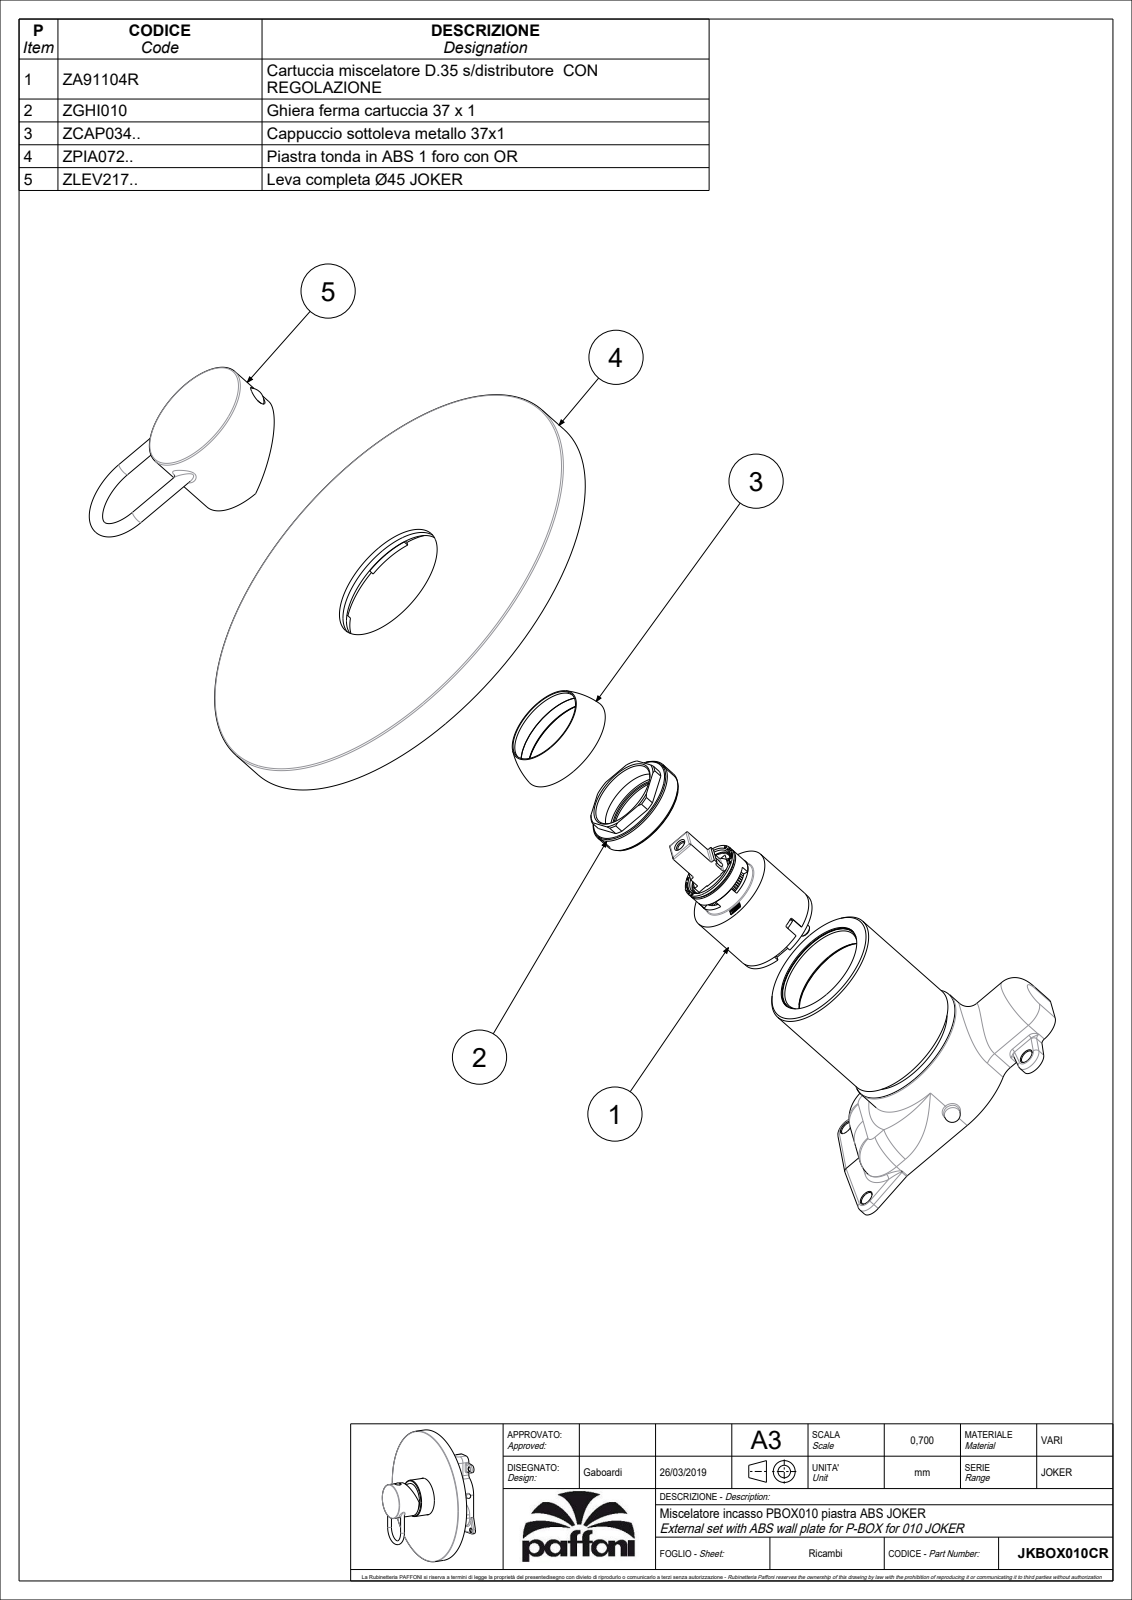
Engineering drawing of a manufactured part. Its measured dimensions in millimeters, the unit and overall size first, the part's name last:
Units: millimetres
Overall size (bounding box): 173 × 173 × 70.49
Round holes (diameter × count): ⌀3 ×1, ⌀4.2 ×1, ⌀5.5 ×1, ⌀30.6 ×1, ⌀36 ×1, ⌀37.5 ×1
Round bosses / shafts (diameter × count): ⌀5 ×2, ⌀173 ×1, ⌀48.1 ×1, ⌀45 ×1
Partial cylindrical surfaces — rounded edges, fillets, slot ends (radius × count): R1.55 ×2, R2.5 ×1
Main face-to-face distances: 13, 66.1, 53.1, 38, 25, 28.1, 9.1, 9.5, 50.6, 37.6
Volume: 341 270 mm³ · Surface area: 76 403 mm²
Bodies: 2 solids, 121 faces (39 planar, 39 cylindrical, 43 other)
Part name (STEP PRODUCT): JKBOX010CR
STEP written by: CREO PARAMETRIC BY PTC INC, 2020044 (CONFIG_CONTROL_DESIGN)
